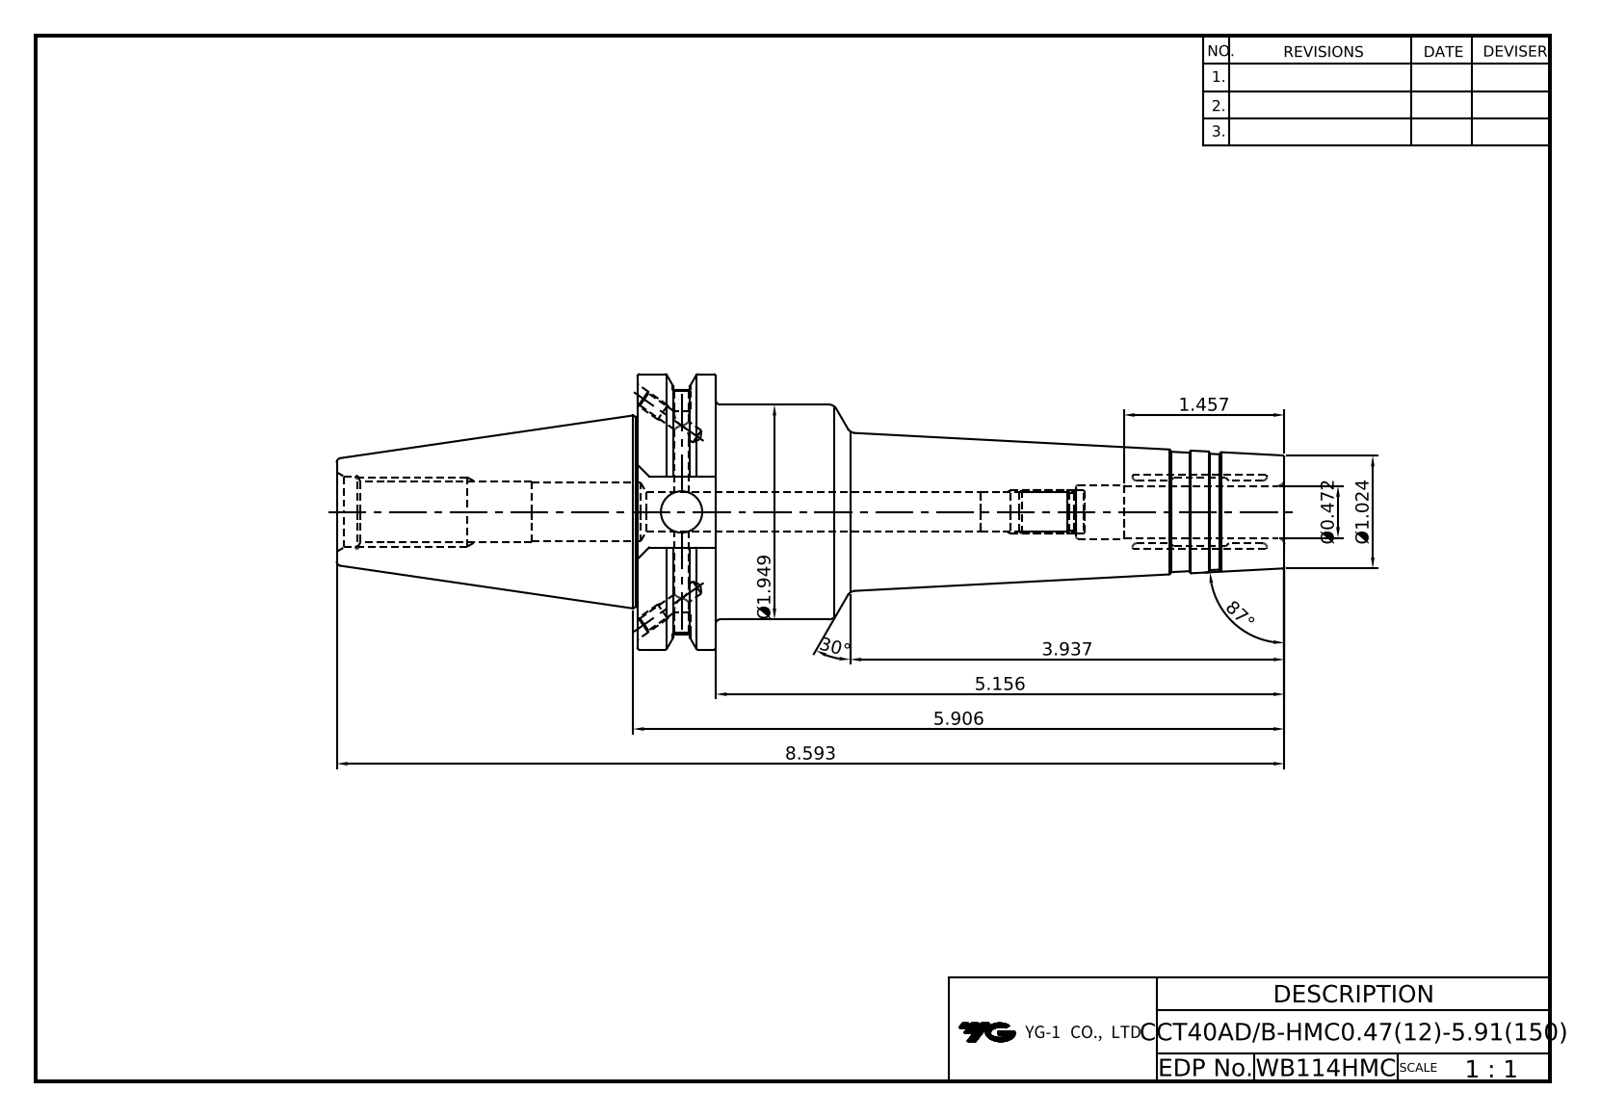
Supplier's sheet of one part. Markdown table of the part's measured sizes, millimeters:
| quantity | value |
| --- | --- |
| part name | LO-CCT40ADB-HMC12-150 |
| STEP written by | Autodesk Inventor 2020 (AUTOMOTIVE_DESIGN) |
| units | millimeters |
| bodies | 1 solid, 106 faces (35 planar, 30 cylindrical, 41 other) |
| overall size | 218.25 × 63.5 × 61.09 |
| volume | 223 871 mm³ |
| surface area | 38 346 mm² |
| round holes (diameter × count) | 3.24 × 4, 4 × 2, 4.2 × 2, 8.92 × 1, 9.53 × 1, 12 × 1, 12.6 × 1, 13 × 1, 13.39 × 1, 16.3 × 1 |
| round bosses / shafts (diameter × count) | 63.5 × 1, 49.5 × 1, 43.8 × 1 |
| partial cylindrical surfaces (radius × count) | 8.19 × 1, 28.15 × 1 |
| main face-to-face distances | 18.05, 149, 130.95, 47.6, 16.38, 69.25, 87.3, 218.25, 81.34, 12.09 |
